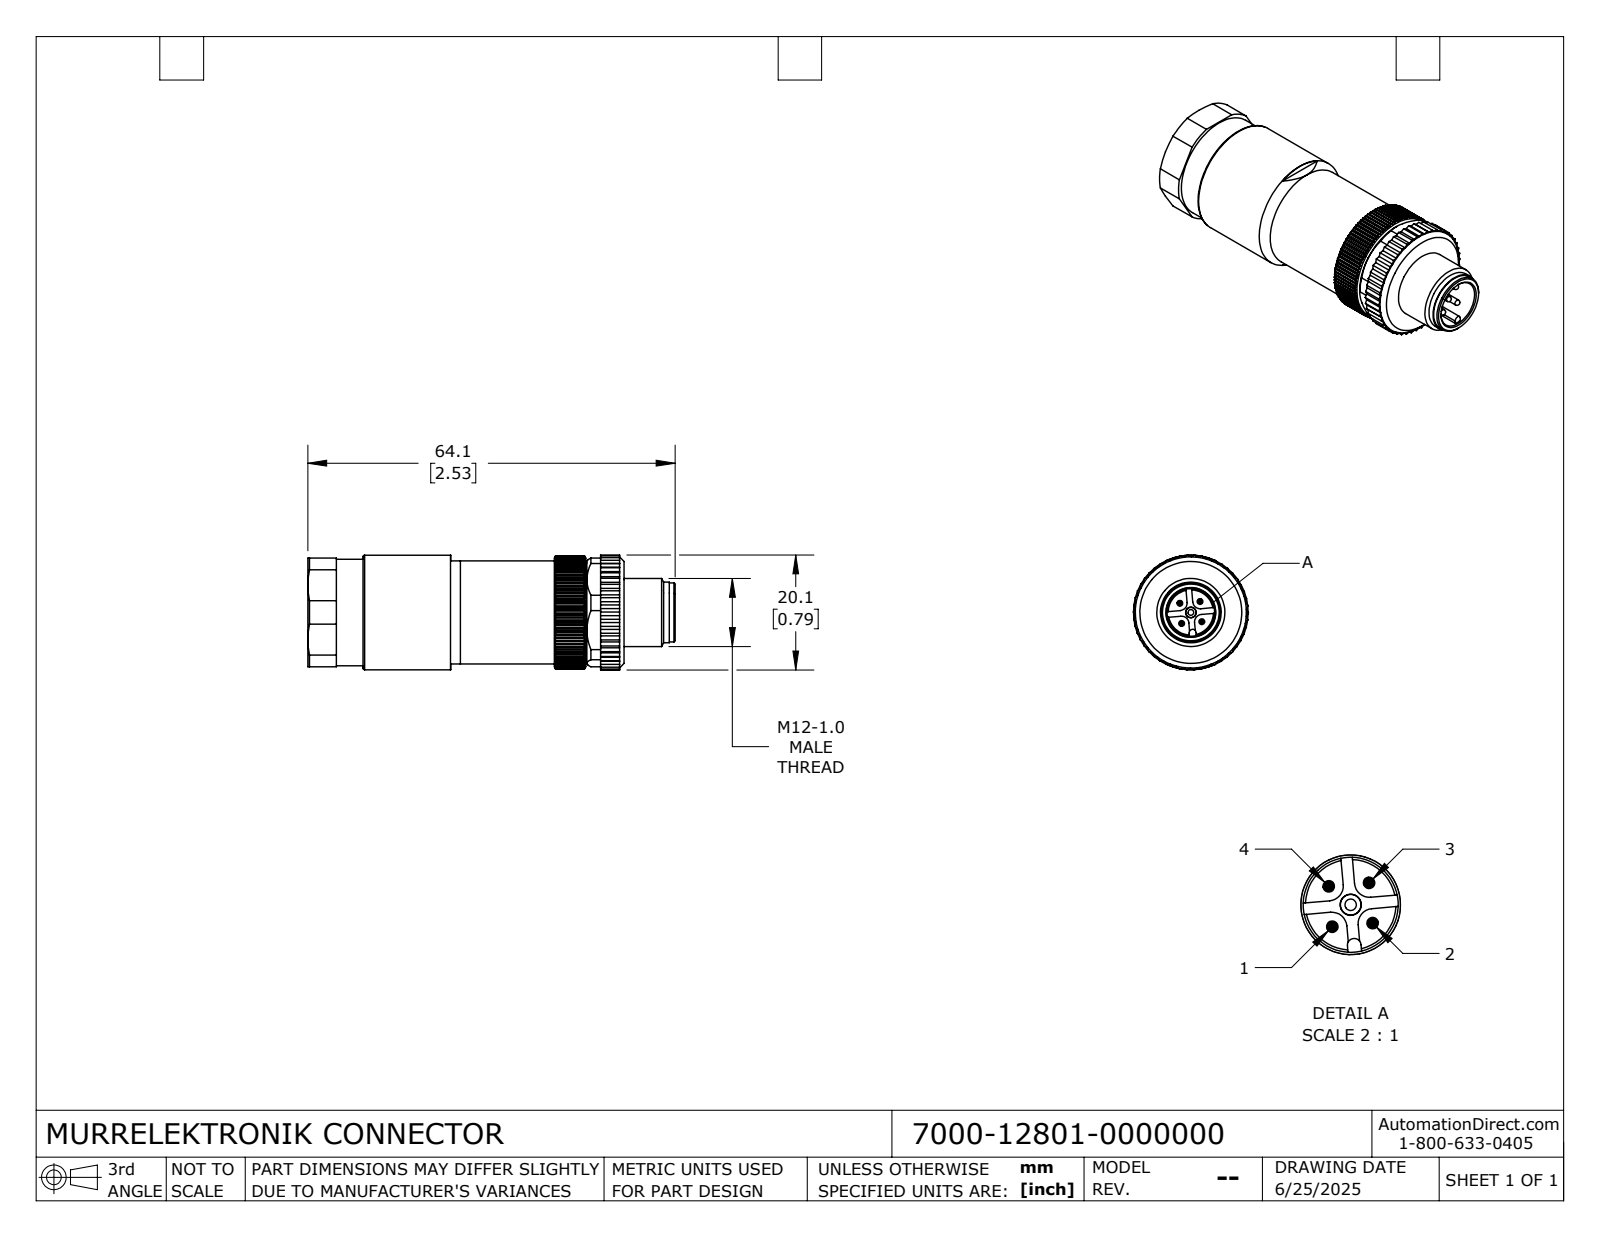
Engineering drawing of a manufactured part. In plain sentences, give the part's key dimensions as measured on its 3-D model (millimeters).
The part is named "7000-12801-0000000". Its 3-D file was written by "SolidWorks 2024 (CONFIG_CONTROL_DESIGN)". It is 1 solid with 546 faces: 346 planar, 152 cylindrical and 48 other. Overall it measures 64.14 by 20.1 by 20.07 millimeters. Its volume is 15 984 cubic millimeters and its surface area 4 960 square millimeters. Round holes: 1 of diameter 1.85, 1 of diameter 8.3, 1 of diameter 11.3. Round bosses or shafts: 5 of diameter 1, 1 of diameter 20, 1 of diameter 19, 1 of diameter 18.6, 1 of diameter 18, 1 of diameter 17.3, 1 of diameter 11.88, 1 of diameter 10.6. Partial cylindrical surfaces (rounded edges, fillets, slot ends): 4 of radius 1.3, 1 of radius 0.6, 1 of radius 9.7, 1 of radius 9.8. The main face-to-face distances are 2.5, 55.24, 17.36, 52.74, 19, 17.64, 17.38, 18, 5.5, 48.54.
